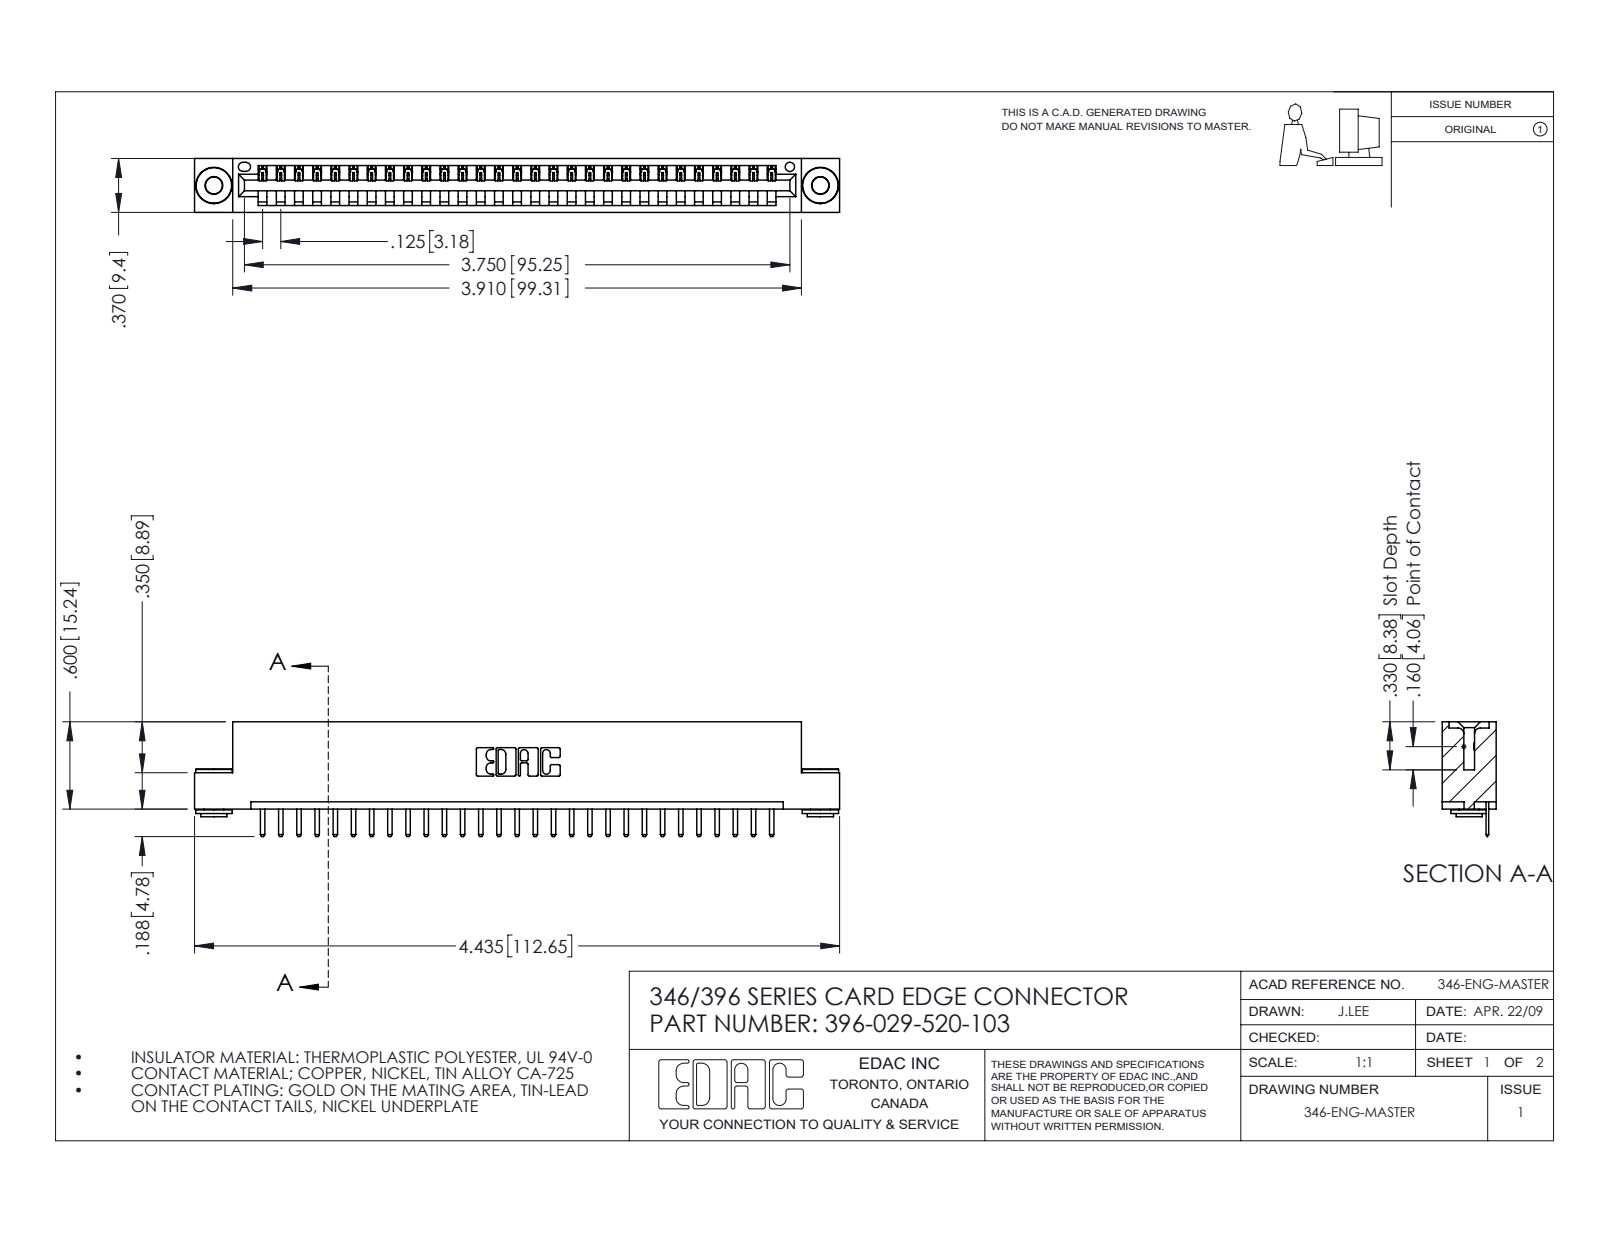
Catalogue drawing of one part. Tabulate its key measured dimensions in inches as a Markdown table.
| quantity | value |
| --- | --- |
| part name | 345-250-002_345-250-002-102; 345-292-001_345-293-120; 396-029-520-103; 346 Part_Flush Mounting Lugs - 0.156 Dia-TH |
| STEP written by | SolidWorks 2016 (CONFIG_CONTROL_DESIGN) |
| units | inches |
| bodies | 32 solids, 1958 faces (1304 planar, 646 cylindrical, 8 other) |
| overall size | 4.435 × 0.788 × 0.37 |
| volume | 0.649 in³ |
| surface area | 20.28 in² |
| round holes (diameter × count) | 0.116 × 2, 0.156 × 2, 0.064 × 1 |
| round bosses / shafts (diameter × count) | 0.25 × 2, 0.18 × 2, 0.136 × 2 |
| partial cylindrical surfaces (radius × count) | 0.01 × 60, 0.006 × 58, 0.01 × 22, 0.007 × 6, 0.031 × 6, 0.026 × 3, 0.031 × 2, 0.04 × 2 |
| main face-to-face distances | 0.048, 0.322, 0.37, 0.25, 0.148, 0.222, 0.1, 0.174, 0.025, 0.072 |
| hole center spacings | 0.246, 3.962, 4.17 |
